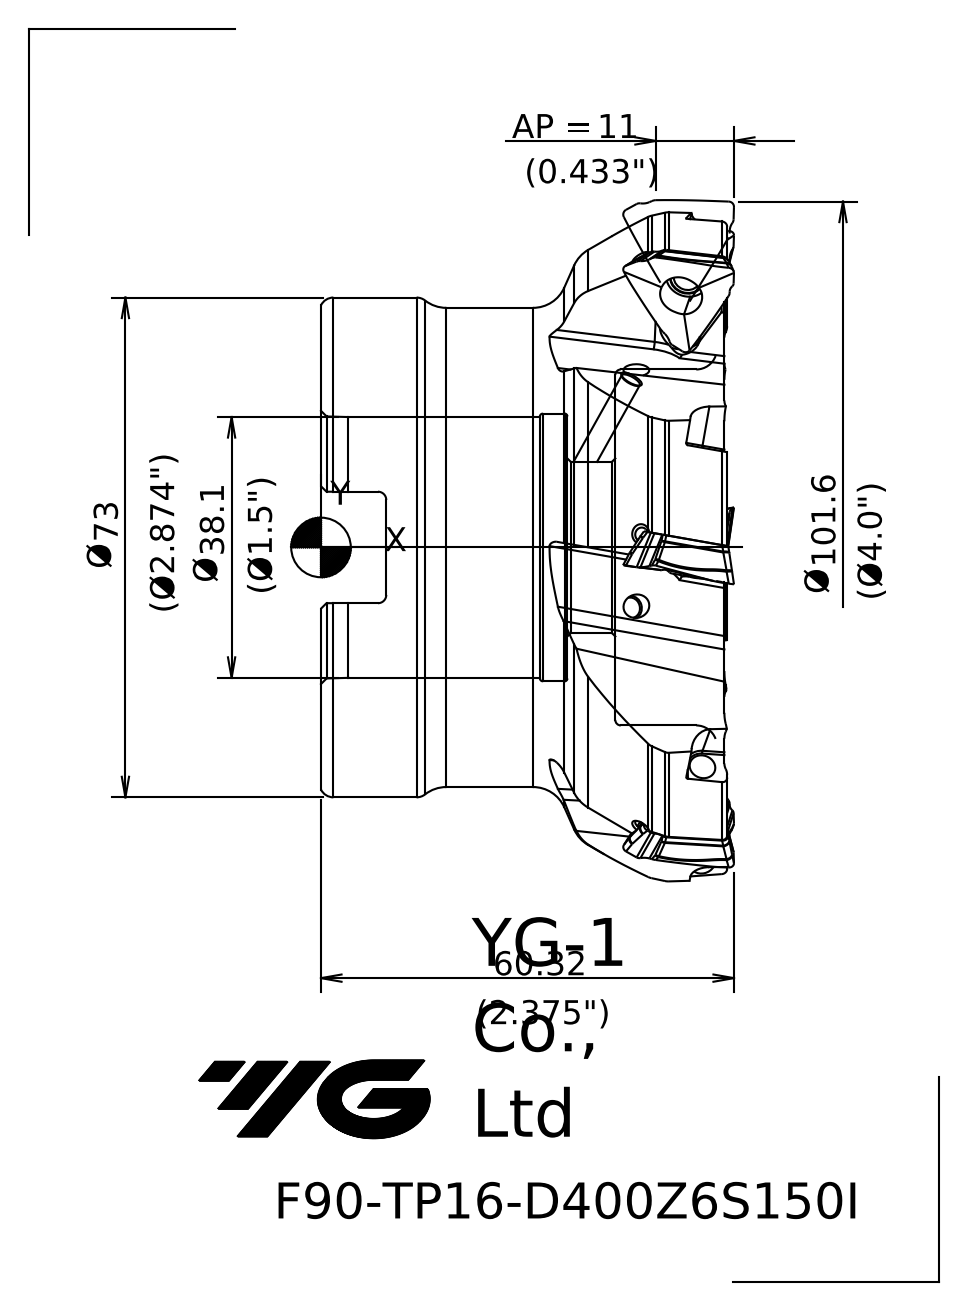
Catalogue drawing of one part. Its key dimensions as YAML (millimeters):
part_name: "1022C79461C3qznd"
step_written_by: "SIEMENS PLM Software NX 10.0 (AP203_CONFIGURATION_CONTROLLED_3D_DESIGN_OF_MECHANICAL_PARTS_AND_ASSEMBLIES_MIM_LF)"
units: millimeters
bodies: {solids: 1, faces: 75, planar: 17, cylindrical: 10, other: 48}
overall_size: [101.73, 101.73, 60.33]
volume: 219328
surface_area: 48290
round_holes:
  - {diameter: 25, count: 1}
  - {diameter: 38.1, count: 1}
  - {diameter: 39.1, count: 1}
  - {diameter: 52, count: 1}
round_bosses_or_shafts:
  - {diameter: 73, count: 1}
  - {diameter: 70, count: 1}
partial_cylinders:
  - {radius: 1.2, count: 2}
face_to_face_distances: [58.93, 15.93, 43, 22.93, 7, 36, 49.39, 33.46, 26.46, 9.54]
